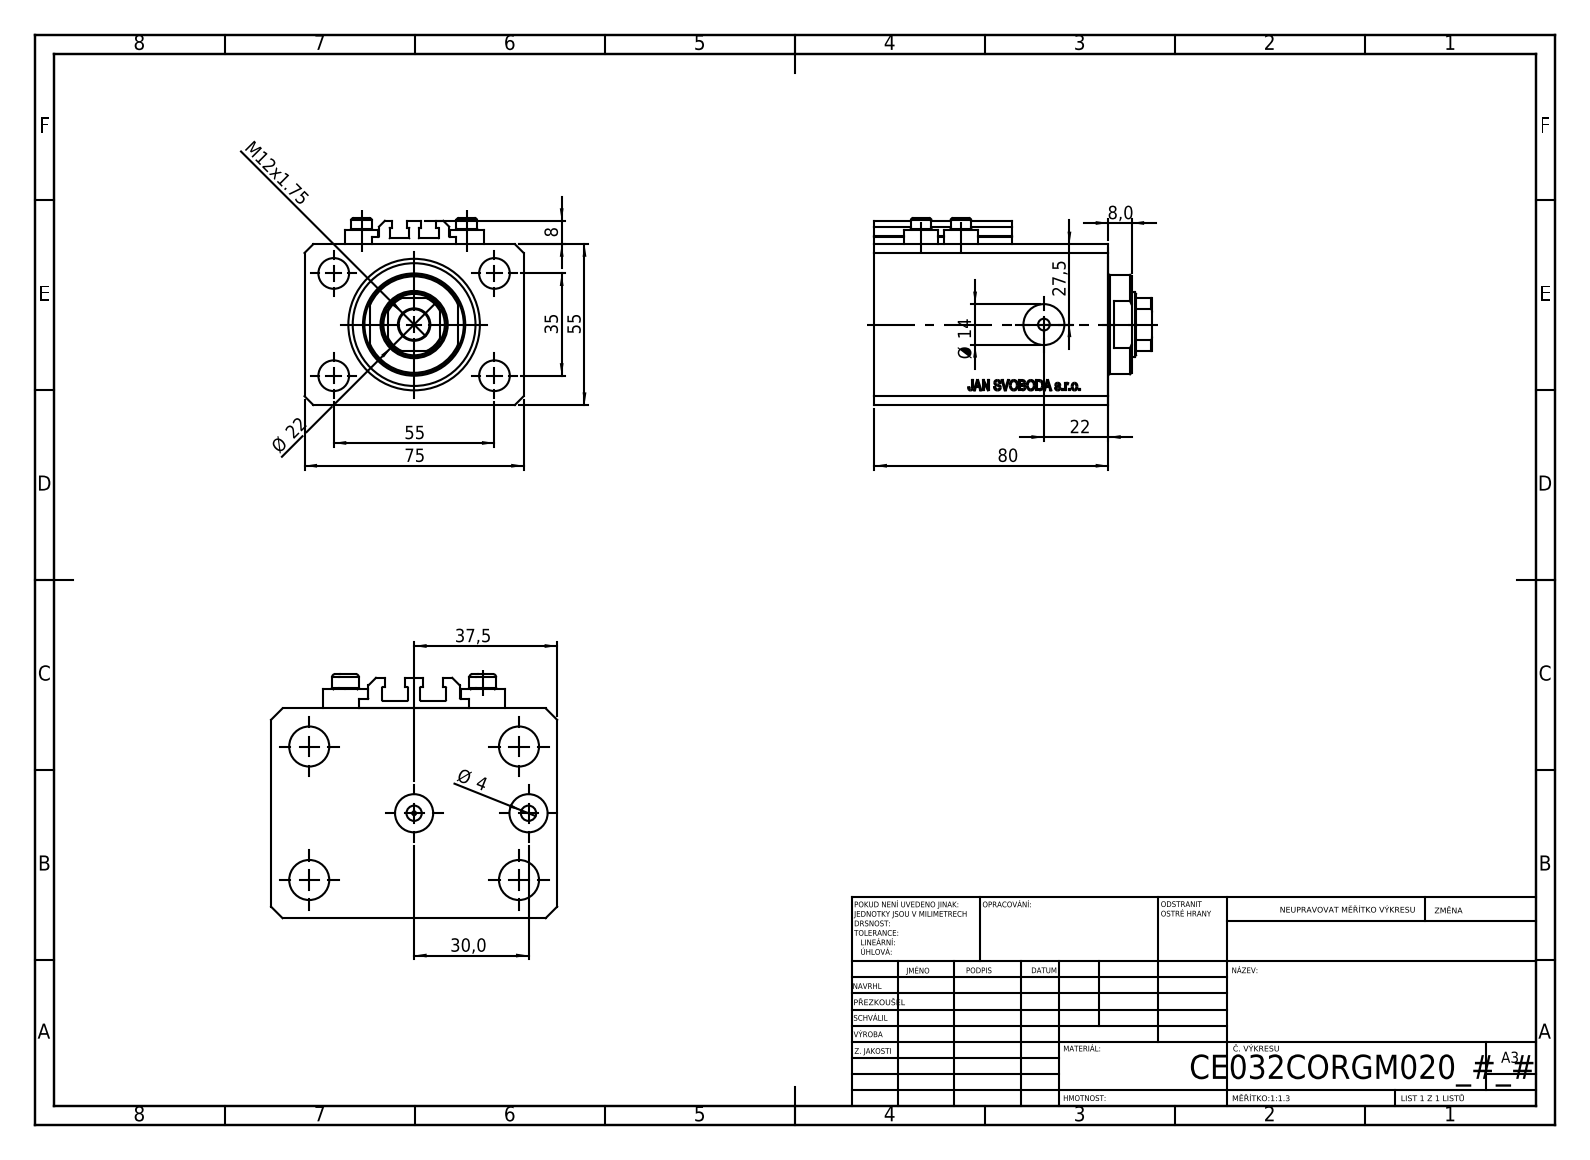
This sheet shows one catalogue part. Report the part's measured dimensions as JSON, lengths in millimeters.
{"part_name": "V250CE_C_VCP; V250CE_VC_C; V250CE_C_Body; ALLEN BOLT V250CE", "step_written_by": "SolidWorks 2019 (CONFIG_CONTROL_DESIGN)", "units": "millimeters", "bodies": {"solids": 8, "faces": 1042, "planar": 504, "cylindrical": 92, "other": 446}, "overall_size": [95, 75, 64], "volume_mm3": 304608, "surface_area_mm2": 71883, "round_holes": [[4, 8], [10.5, 5], [10, 2], [14, 2], [1.25, 1], [22, 1], [32, 1], [45, 1]], "round_bosses_or_shafts": [[11.6, 4], [7, 4], [34, 1]], "partial_cylinders_radius": [[0.2, 10], [10.5, 1]], "face_to_face_distances": [55, 75, 80, 15, 65, 9.9, 55.1, 70.1, 3, 8], "hole_center_spacings": [32.6, 36, 13.6, 17.68, 35, 38.48, 55, 60.1]}
